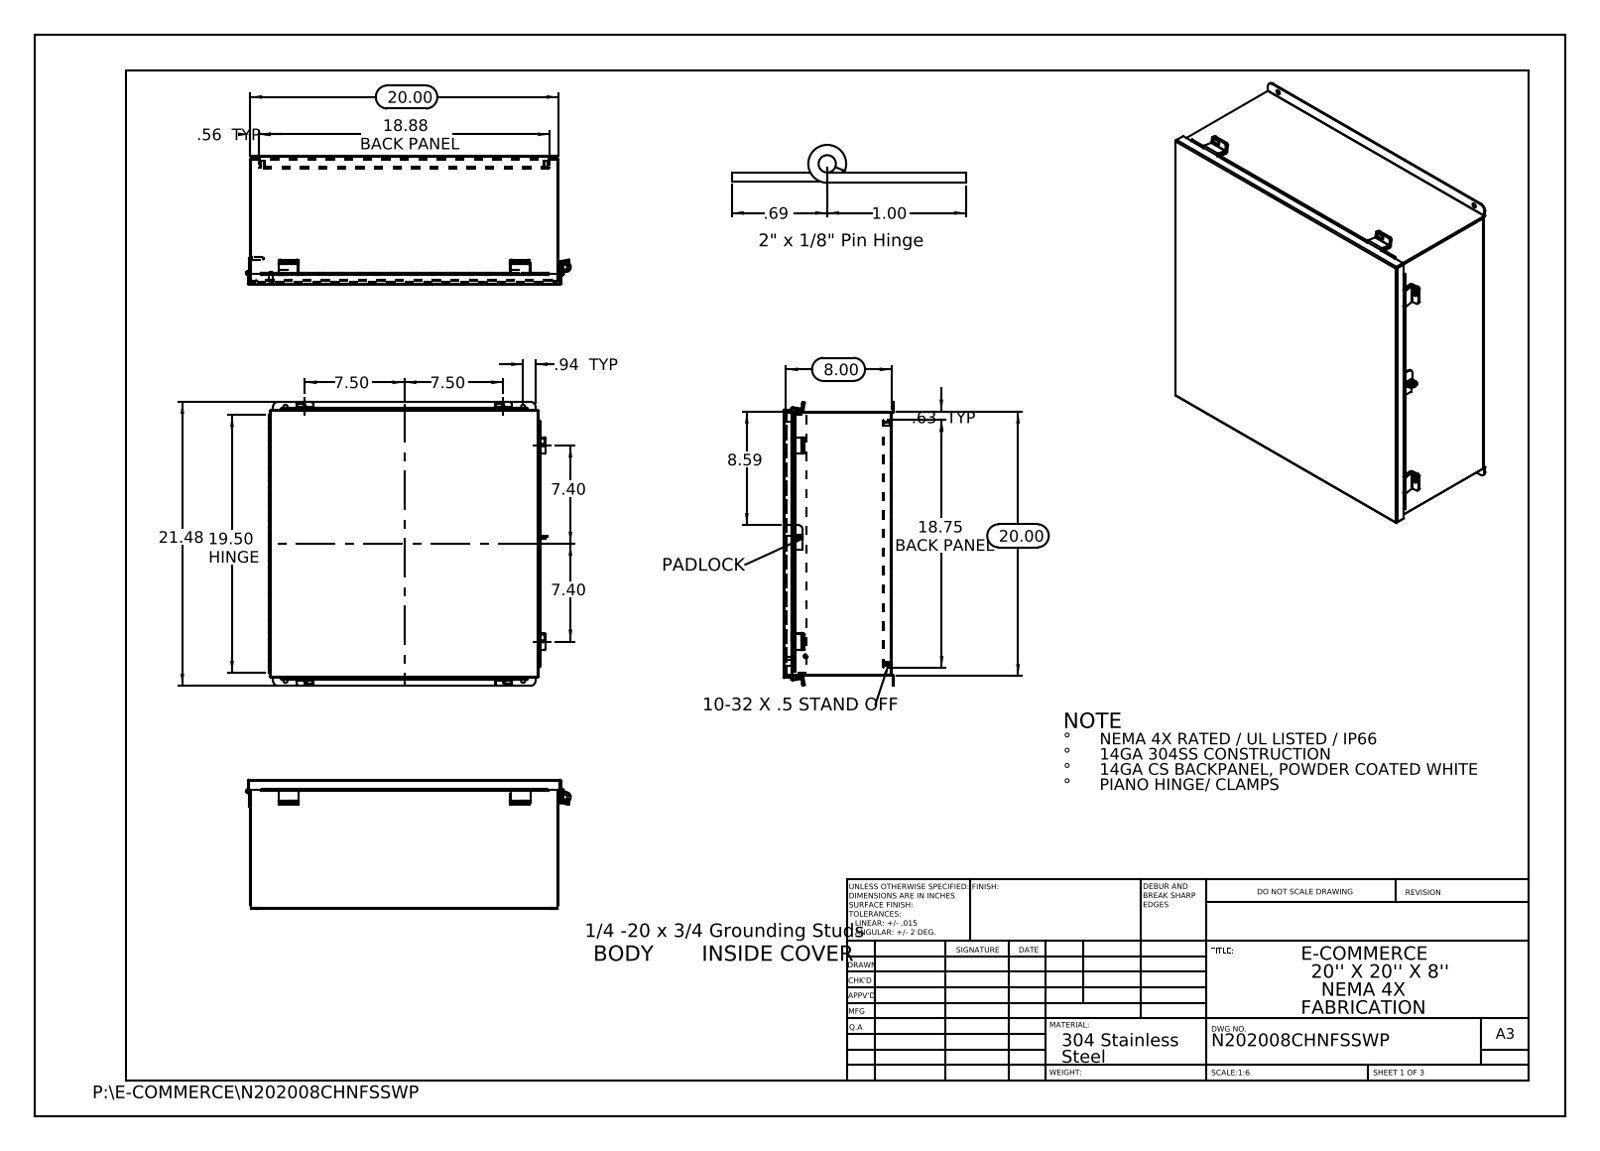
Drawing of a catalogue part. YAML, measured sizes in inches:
part_name: "N202008CHNFSSWP JIC Backpanel; N202008CHNFSSWP Hinge Body Side; N202008CHNFSSWP JIC_Standoff; HW-CLH-JH-20104 (+8 more)"
step_written_by: "SolidWorks 2013 (CONFIG_CONTROL_DESIGN)"
units: inches
bodies: {solids: 27, faces: 938, planar: 579, cylindrical: 339, other: 20}
overall_size: [21.476, 21.072, 8.39]
volume: 147.2
surface_area: 3987
round_holes:
  - {diameter: 0.25, count: 10}
  - {diameter: 0.187, count: 4}
  - {diameter: 0.312, count: 4}
  - {diameter: 0.125, count: 1}
  - {diameter: 0.125, count: 1}
  - {diameter: 0.373, count: 1}
  - {diameter: 0.375, count: 1}
round_bosses_or_shafts:
  - {diameter: 0.313, count: 4}
  - {diameter: 0.315, count: 2}
  - {diameter: 0.236, count: 2}
  - {diameter: 0.273, count: 1}
  - {diameter: 0.25, count: 1}
partial_cylinders:
  - {radius: 0.125, count: 24}
  - {radius: 0.013, count: 13}
  - {radius: 0.009, count: 12}
  - {radius: 0.088, count: 12}
  - {radius: 0.133, count: 12}
  - {radius: 0.083, count: 6}
  - {radius: 0.1, count: 6}
  - {radius: 0.375, count: 4}
face_to_face_distances: [0.075, 8.128, 19.925, 8.053, 8.203, 7.628, 0.575, 0.5, 7.553, 0.649]
hole_center_spacings: [1.315, 18.222, 19.427, 26.603, 15, 17.976, 18.126, 18.375]
